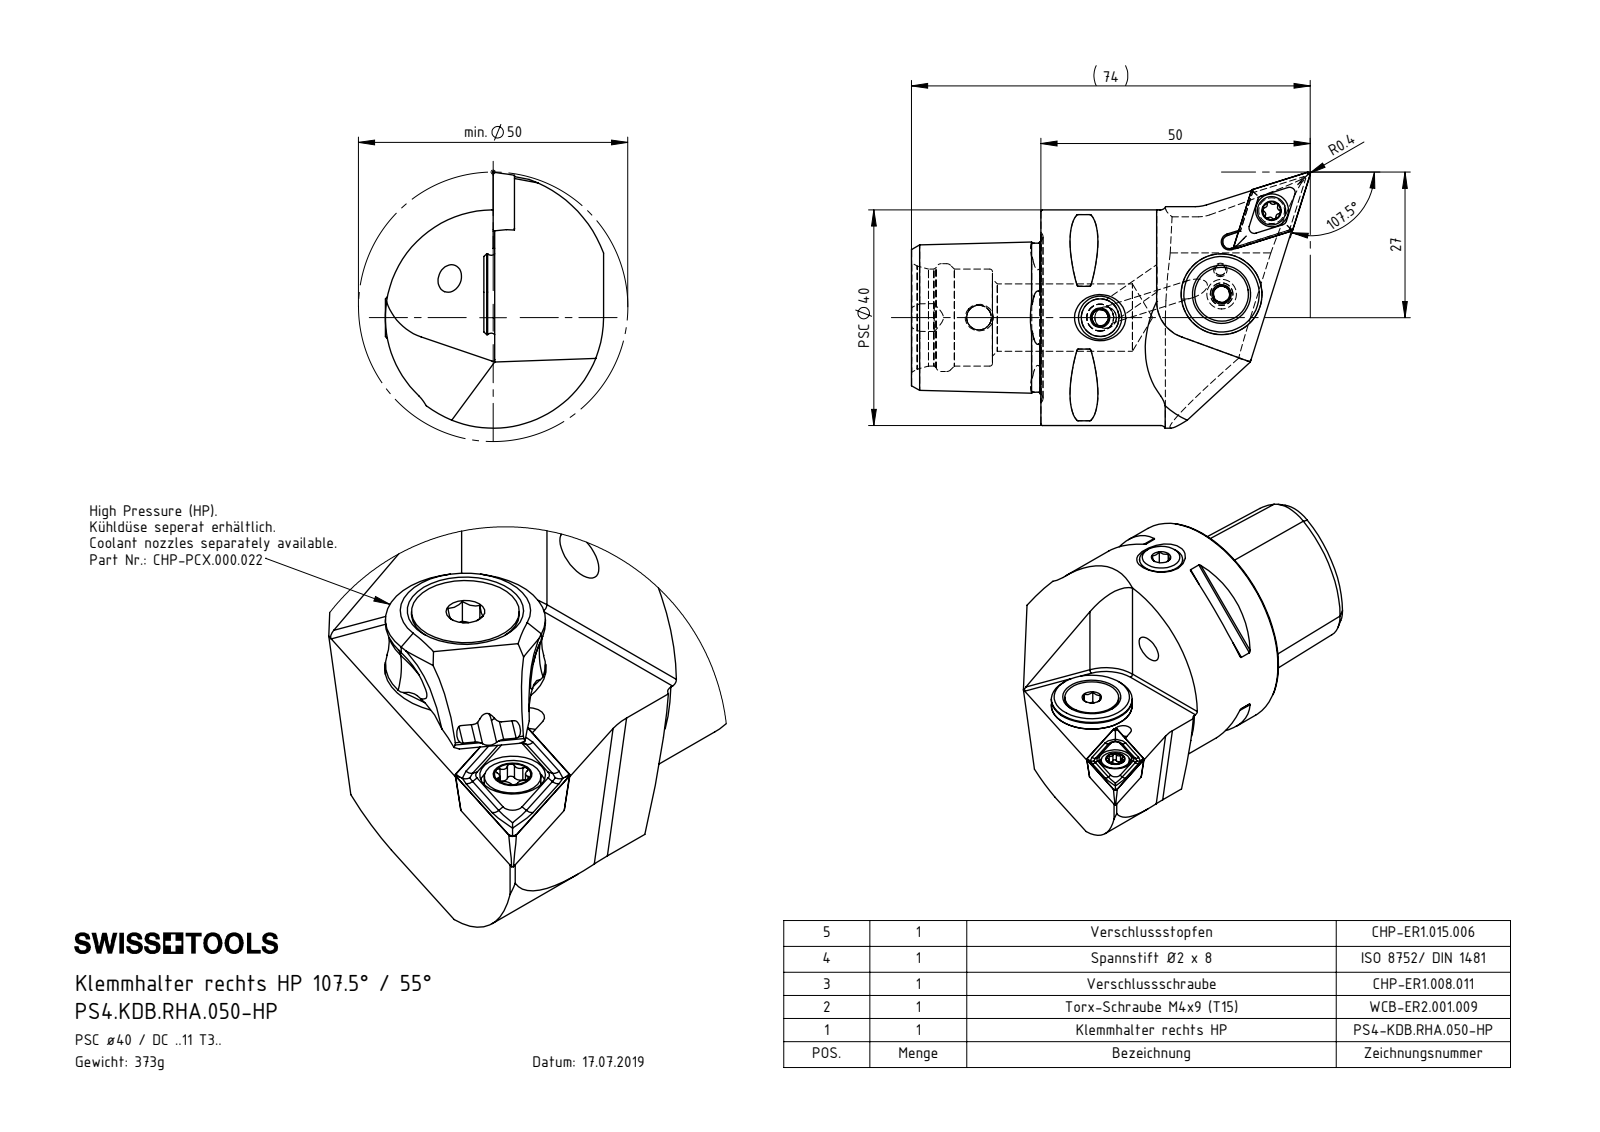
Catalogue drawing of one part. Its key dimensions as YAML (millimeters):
part_name: "WCB-ER2.001.009_A; CHP-ER1.015.006_A; CHP-ER1.008.011_A; DCMT11T304 (+6 more)"
step_written_by: "SolidWorks 2017 (AUTOMOTIVE_DESIGN)"
units: millimeters
bodies: {solids: 8, faces: 385, planar: 91, cylindrical: 99, other: 195}
overall_size: [74.01, 47.5, 40.5]
volume: 47579
surface_area: 15103
round_holes:
  - {diameter: 3.3, count: 2}
  - {diameter: 4.2, count: 2}
  - {diameter: 1.2, count: 1}
  - {diameter: 2, count: 1}
  - {diameter: 2.5, count: 1}
  - {diameter: 3, count: 1}
  - {diameter: 4, count: 1}
  - {diameter: 4.4, count: 1}
  - {diameter: 4.6, count: 1}
  - {diameter: 5, count: 1}
  - {diameter: 5.2, count: 1}
  - {diameter: 6.1, count: 1}
round_bosses_or_shafts:
  - {diameter: 40, count: 1}
  - {diameter: 15, count: 1}
  - {diameter: 13.4, count: 1}
  - {diameter: 10, count: 1}
  - {diameter: 8, count: 1}
  - {diameter: 5.5, count: 1}
  - {diameter: 5.25, count: 1}
  - {diameter: 5, count: 1}
partial_cylinders:
  - {radius: 0.3, count: 8}
  - {radius: 0.34, count: 6}
  - {radius: 0.59, count: 6}
  - {radius: 0.5, count: 2}
  - {radius: 7, count: 2}
  - {radius: 1.25, count: 1}
  - {radius: 3, count: 1}
  - {radius: 20.5, count: 1}
face_to_face_distances: [4.5, 21.5, 15.7, 20.2, 24, 45.5, 16.53, 0.83, 3.67, 15.52]
hole_center_spacings: [1, 4.5, 14.54, 14.67, 18.05, 18.18, 21.97, 22.5]
